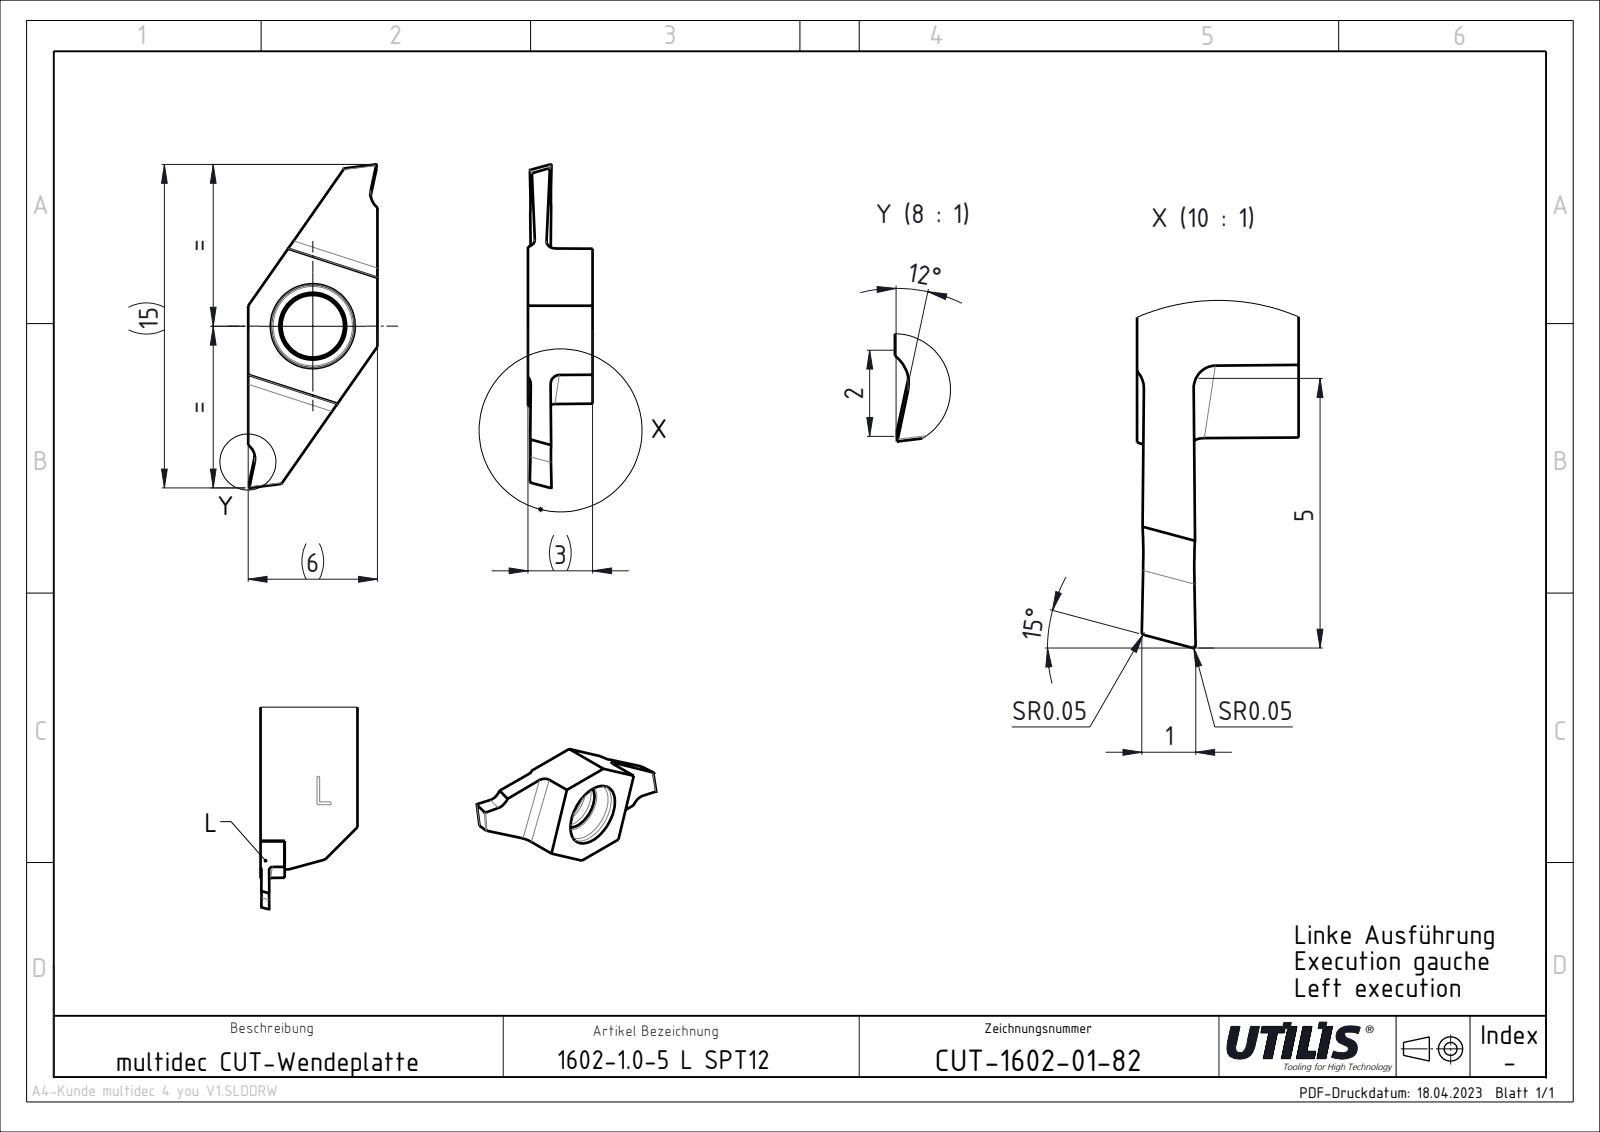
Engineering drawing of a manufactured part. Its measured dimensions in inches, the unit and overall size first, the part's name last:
Units: inches
Overall size (bounding box): 0.591 × 0.236 × 0.118
Round holes (diameter × count): ⌀0.114 ×1
Partial cylindrical surfaces — rounded edges, fillets, slot ends (radius × count): R0.016 ×4
Main face-to-face distances: 0.236, 0.118, 0.033
Volume: 0.006 in³ · Surface area: 0.324 in²
Bodies: 1 solid, 23 faces (14 planar, 9 cylindrical, 0 other)
Part name (STEP PRODUCT): 1-CUT-1602-01-82 stp
STEP written by: SolidWorks 2022 (AUTOMOTIVE_DESIGN)
